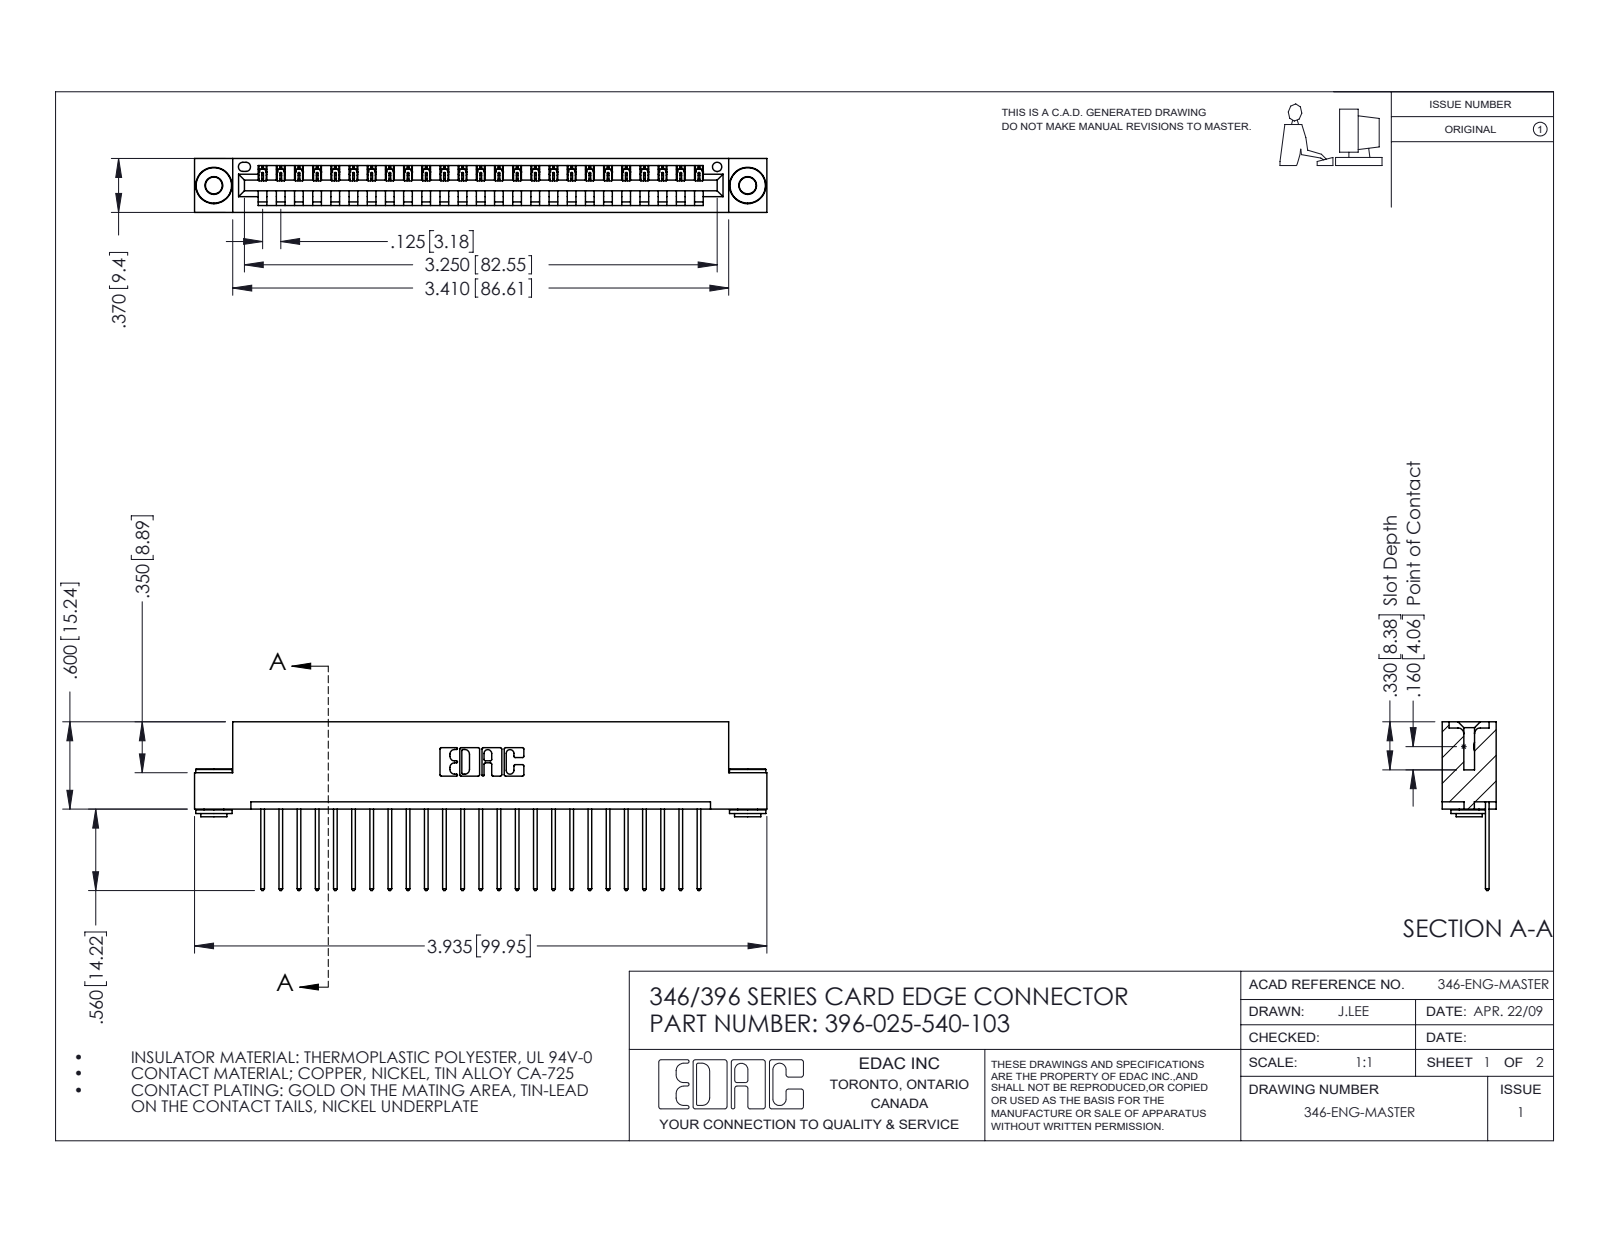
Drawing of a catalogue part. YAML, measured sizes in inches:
part_name: "396-025-540-103; 345-250-002_345-250-002-102; 345-292-001_345-293-140; 346 Part_Flush Mounting Lugs - 0.156 Dia-TH"
step_written_by: "SolidWorks 2016 (CONFIG_CONTROL_DESIGN)"
units: inches
bodies: {solids: 28, faces: 1610, planar: 1086, cylindrical: 516, other: 8}
overall_size: [3.935, 1.16, 0.37]
volume: 0.58
surface_area: 18.85
round_holes:
  - {diameter: 0.116, count: 2}
  - {diameter: 0.156, count: 2}
  - {diameter: 0.064, count: 1}
round_bosses_or_shafts:
  - {diameter: 0.25, count: 2}
  - {diameter: 0.18, count: 2}
  - {diameter: 0.136, count: 2}
partial_cylinders:
  - {radius: 0.006, count: 50}
  - {radius: 0.01, count: 50}
  - {radius: 0.01, count: 22}
  - {radius: 0.007, count: 6}
  - {radius: 0.031, count: 6}
  - {radius: 0.026, count: 3}
  - {radius: 0.031, count: 2}
  - {radius: 0.04, count: 2}
face_to_face_distances: [0.048, 0.322, 0.25, 0.37, 0.025, 0.072, 0.298, 0.148, 0.222, 0.1]
hole_center_spacings: [0.246, 3.462, 3.67]
